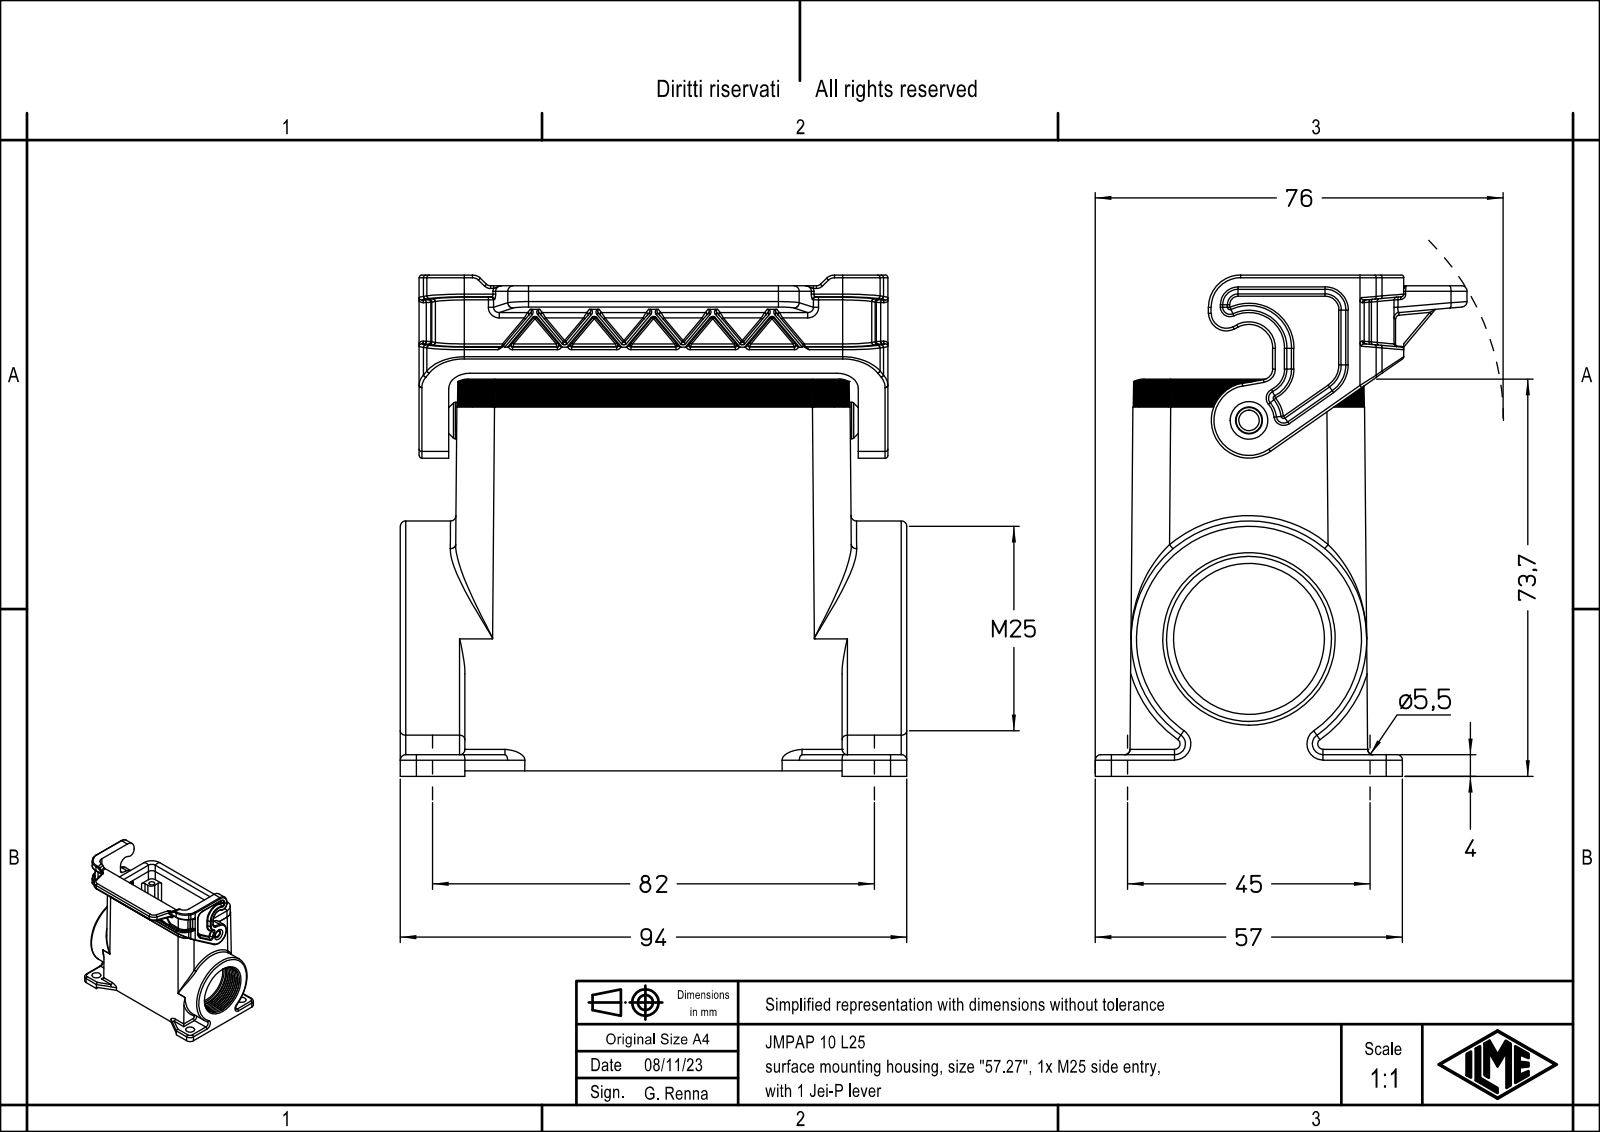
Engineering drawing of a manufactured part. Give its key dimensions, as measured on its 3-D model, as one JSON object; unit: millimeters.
{"part_name": "JMPAP 10 L25", "step_written_by": "Creo Elements/Direct Modeling 20.1B 02-Apr-2019 (C) Parametric Technology GmbH (AUTOMOTIVE_DESIGN)", "units": "millimeters", "bodies": {"solids": 1, "faces": 762, "planar": 169, "cylindrical": 316, "other": 277}, "overall_size": [94, 93, 69], "volume_mm3": 130787, "surface_area_mm2": 52125, "round_holes": [[3, 4], [3.5, 4], [5.5, 4], [4.8, 1], [23.6, 1]], "round_bosses_or_shafts": [[43.75, 1], [6.8, 1]], "partial_cylinders_radius": [[0.5, 77], [0.3, 71], [1, 23], [3, 16], [2, 11], [7, 9], [1.5, 8], [4, 8]], "face_to_face_distances": [3, 85, 1, 4, 9, 94, 87, 3.5, 5.5, 91], "hole_center_spacings": [15.4, 38.11, 70.08, 78.27, 27, 45, 57, 63.07]}
